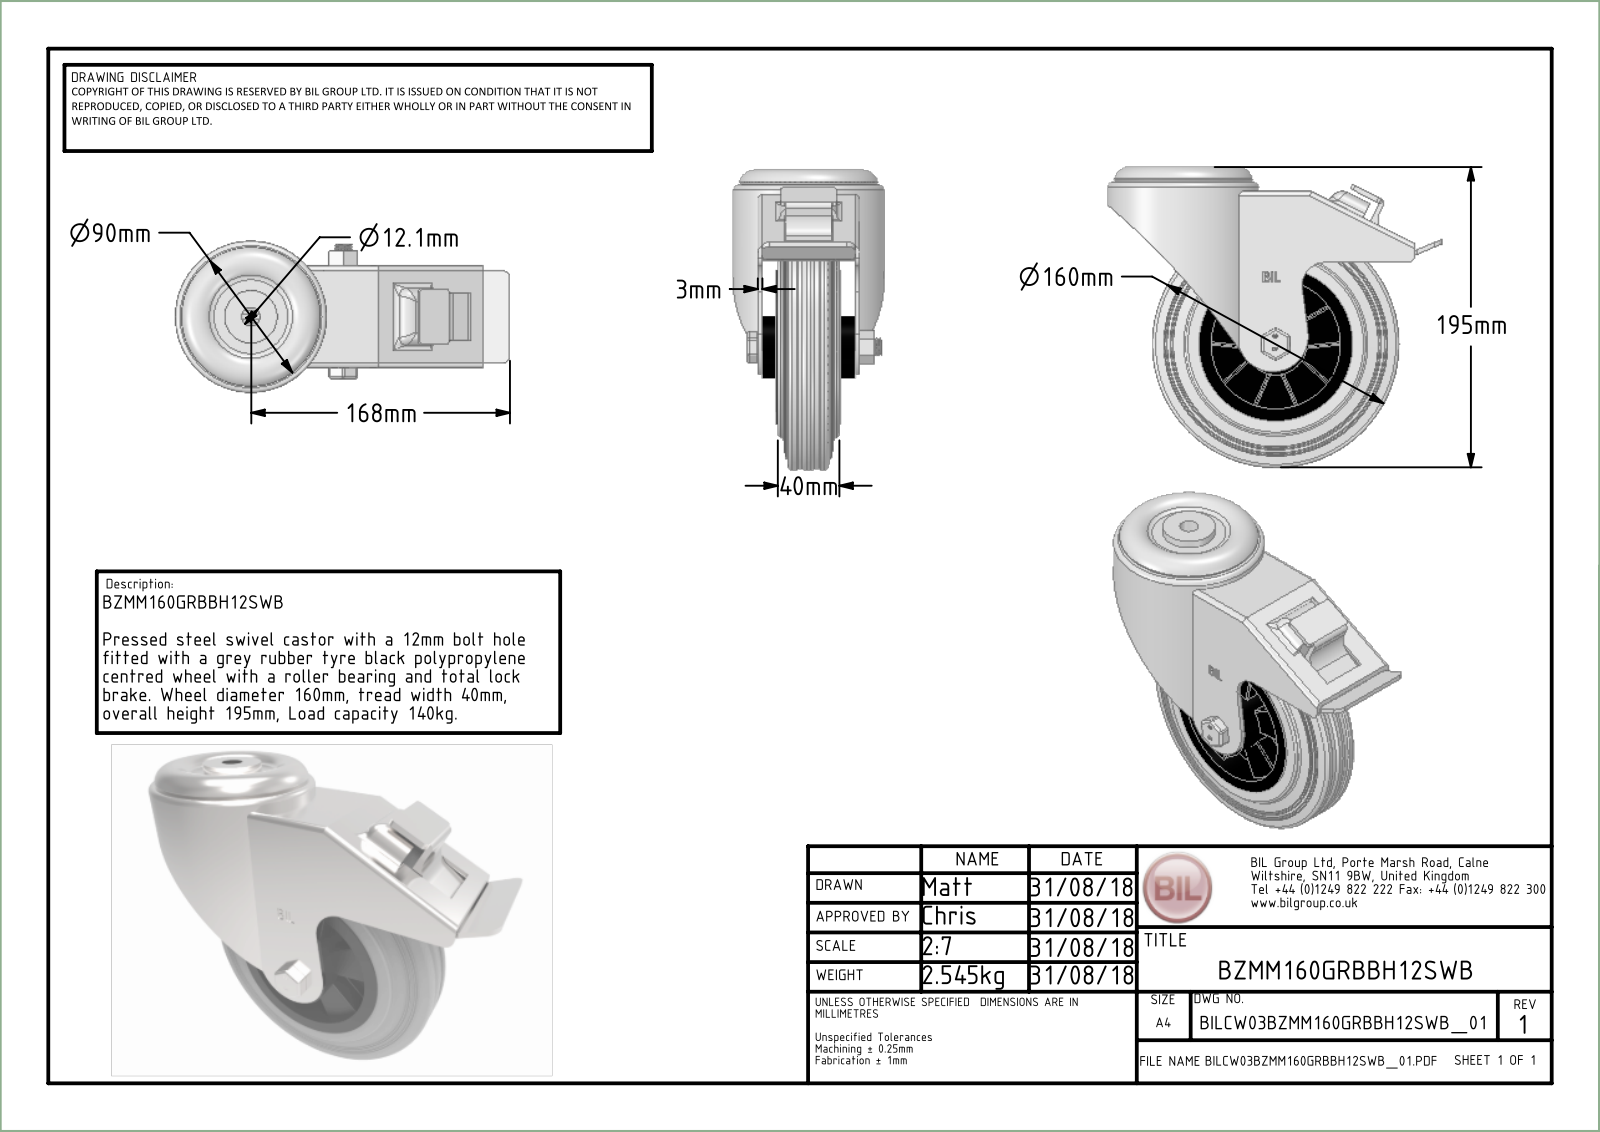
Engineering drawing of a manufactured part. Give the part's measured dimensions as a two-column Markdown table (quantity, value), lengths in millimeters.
| quantity | value |
| --- | --- |
| part name | BZMM160GRBBH12SWB v3; BZMM150ASBH12SWB v1; ZINC PLATED, PRESSED STEEL TOP PLATE; ZINC PLATED, PRESSED STEEL FORKS (+8 more) |
| STEP written by | Autodesk Translation Framework v13.20.0.188 (AUTOMOTIVE_DESIGN) |
| units | millimeters |
| bodies | 23 solids, 935 faces (364 planar, 217 cylindrical, 354 other) |
| overall size | 223 × 195 × 110 |
| volume | 779 728 mm³ |
| surface area | 279 247 mm² |
| round holes (diameter × count) | 8 × 2, 34 × 2, 12 × 1, 12.1 × 1, 12.2 × 1, 12.5 × 1, 14 × 1, 20 × 1, 33.5 × 1, 35 × 1, 52.5 × 1, 65.5 × 1 |
| round bosses / shafts (diameter × count) | 7.5 × 8, 40 × 2, 158.4 × 1, 110 × 1, 101 × 1, 77 × 1, 34.9 × 1, 25 × 1 |
| partial cylindrical surfaces (radius × count) | 0.5 × 24, 1 × 18, 1.5 × 12, 3 × 8, 2 × 3, 2.5 × 3, 4 × 2, 6 × 2 |
| main face-to-face distances | 3, 63, 4.75, 1.5, 2.5, 7.75, 1.75, 60, 3.25, 11.5 |
| hole center spacings | 69 |
